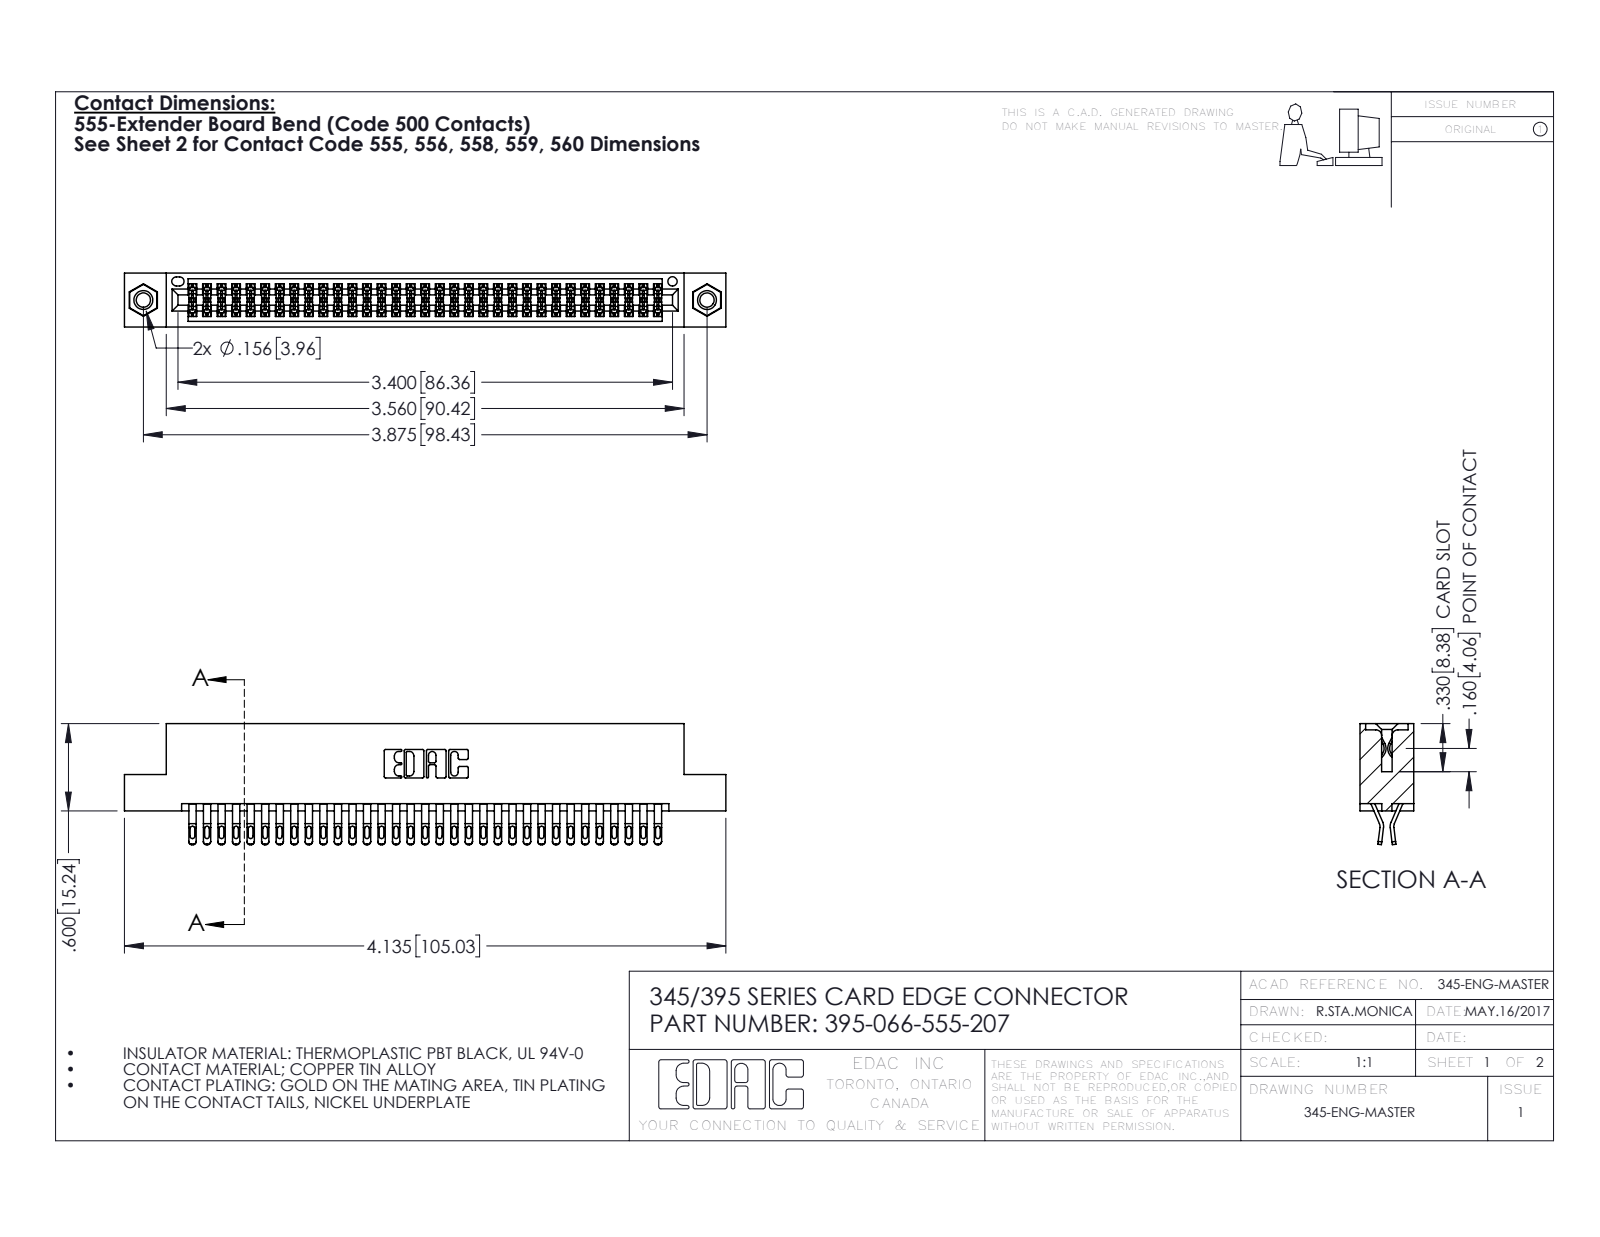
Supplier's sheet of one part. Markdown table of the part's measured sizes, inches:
| quantity | value |
| --- | --- |
| part name | 345-292-001_555 Tail; 395-066-555-207; 345-250-001_345-250-005-103; 345 Part_Flush Mounting Lugs - 0.156 Dia-TI |
| STEP written by | SolidWorks 2016 (CONFIG_CONTROL_DESIGN) |
| units | inches |
| bodies | 69 solids, 3882 faces (2158 planar, 1708 cylindrical, 16 other) |
| overall size | 4.135 × 0.832 × 0.37 |
| volume | 0.628 in³ |
| surface area | 24.4 in² |
| round holes (diameter × count) | 0.098 × 2, 0.125 × 2, 0.156 × 2, 0.064 × 1 |
| round bosses / shafts (diameter × count) | 0.155 × 2 |
| partial cylindrical surfaces (radius × count) | 0.016 × 165, 0.02 × 132, 0.006 × 99, 0.01 × 22, 0.007 × 6, 0.031 × 6, 0.026 × 3, 0.01 × 2 |
| main face-to-face distances | 0.072, 0.298, 0.2, 0.37, 0.025, 0.098, 0.272, 0.225, 0.175, 0.149 |
| hole center spacings | 0.27, 3.64, 3.875 |
